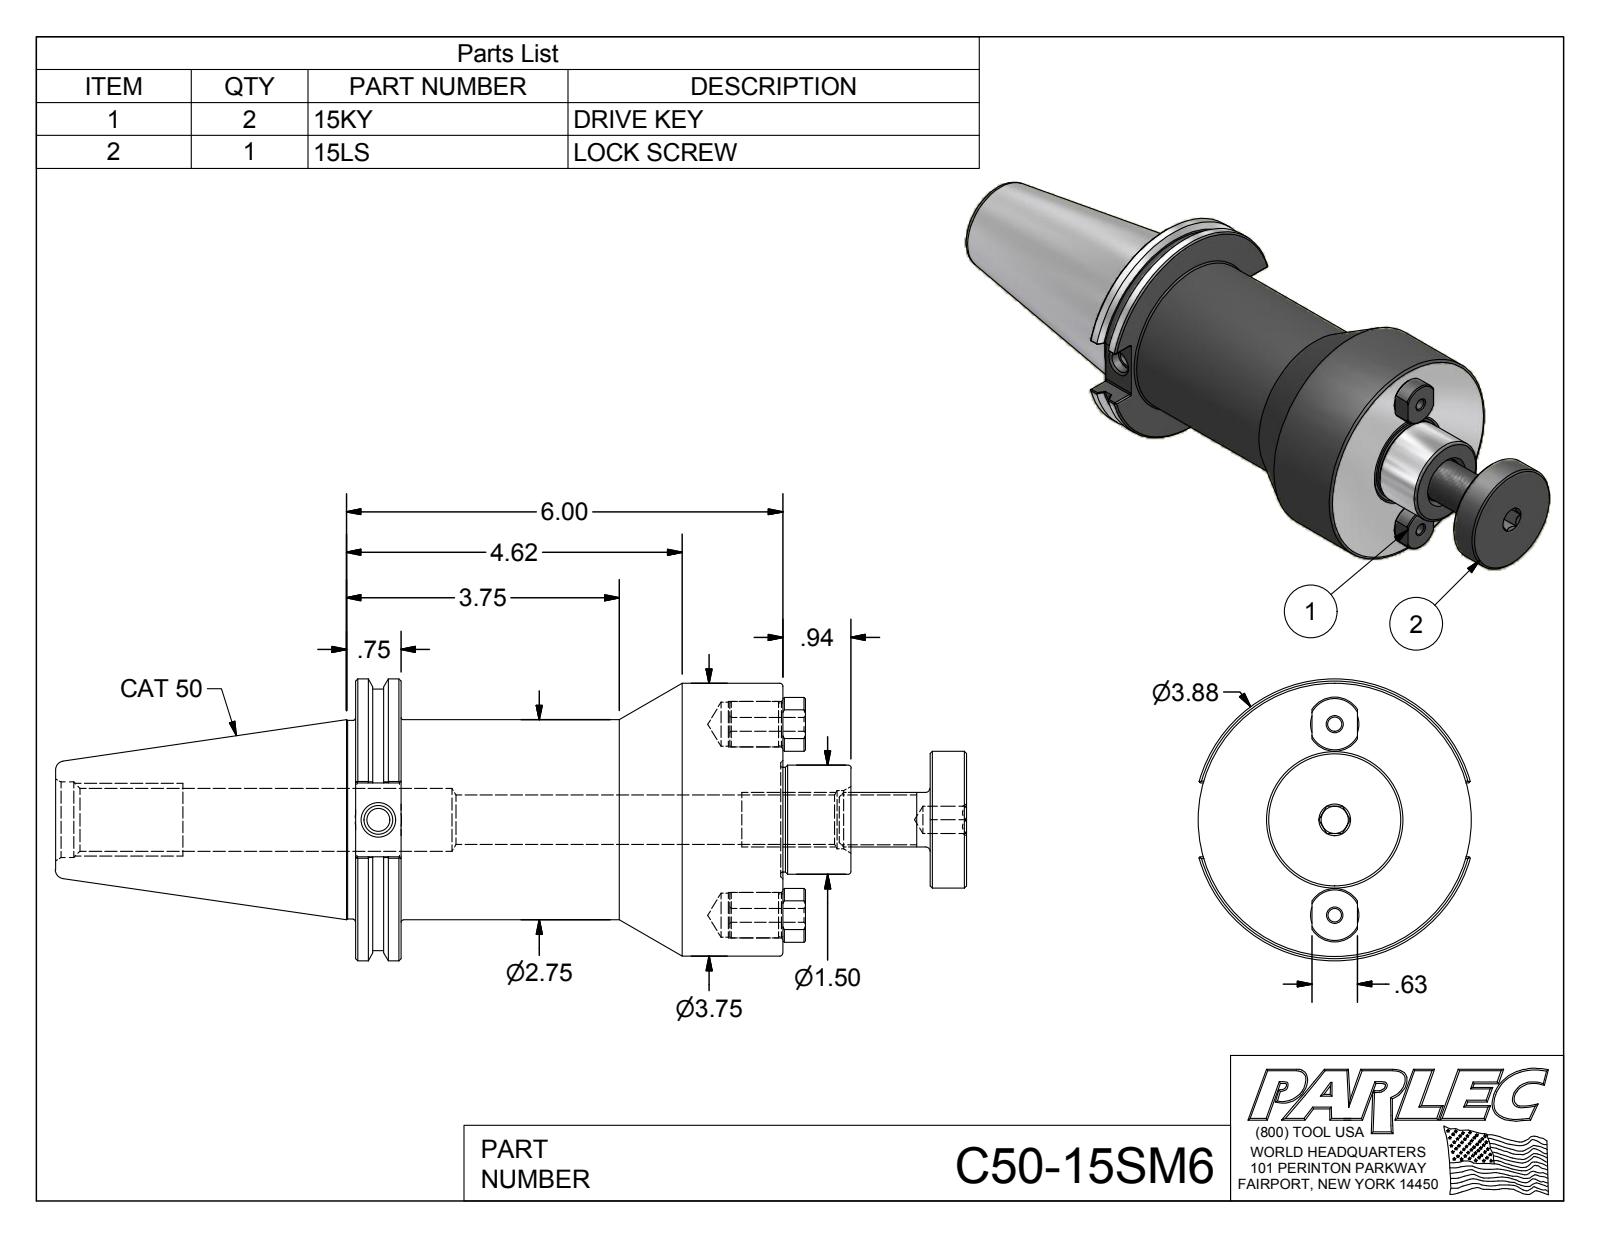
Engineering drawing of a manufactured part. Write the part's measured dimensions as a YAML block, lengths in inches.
part_name: "C50-15SM6; C50-15SM6-1; 15LS; 15KY"
step_written_by: "Autodesk Inventor 2012 (AUTOMOTIVE_DESIGN)"
units: inches
bodies: {solids: 4, faces: 166, planar: 62, cylindrical: 46, other: 58}
overall_size: [12.525, 3.875, 3.75]
volume: 60.82
surface_area: 166.1
round_holes:
  - {diameter: 0.19, count: 2}
  - {diameter: 0.604, count: 2}
  - {diameter: 0.624, count: 2}
  - {diameter: 0.315, count: 1}
  - {diameter: 0.375, count: 1}
  - {diameter: 0.399, count: 1}
  - {diameter: 0.682, count: 1}
  - {diameter: 0.8, count: 1}
  - {diameter: 0.865, count: 1}
  - {diameter: 1.038, count: 1}
round_bosses_or_shafts:
  - {diameter: 0.626, count: 2}
  - {diameter: 0.59, count: 2}
  - {diameter: 3.875, count: 1}
  - {diameter: 3.75, count: 1}
  - {diameter: 3.594, count: 1}
  - {diameter: 2.75, count: 1}
  - {diameter: 2.73, count: 1}
  - {diameter: 1.88, count: 1}
partial_cylinders:
  - {radius: 0.02, count: 12}
  - {radius: 0.37, count: 2}
face_to_face_distances: [0.625, 5.875, 5.25, 8.4, 7.775, 2.525, 7.9, 7.275, 2.025, 0.5]
hole_center_spacings: [1.312, 1.312, 2.624]
